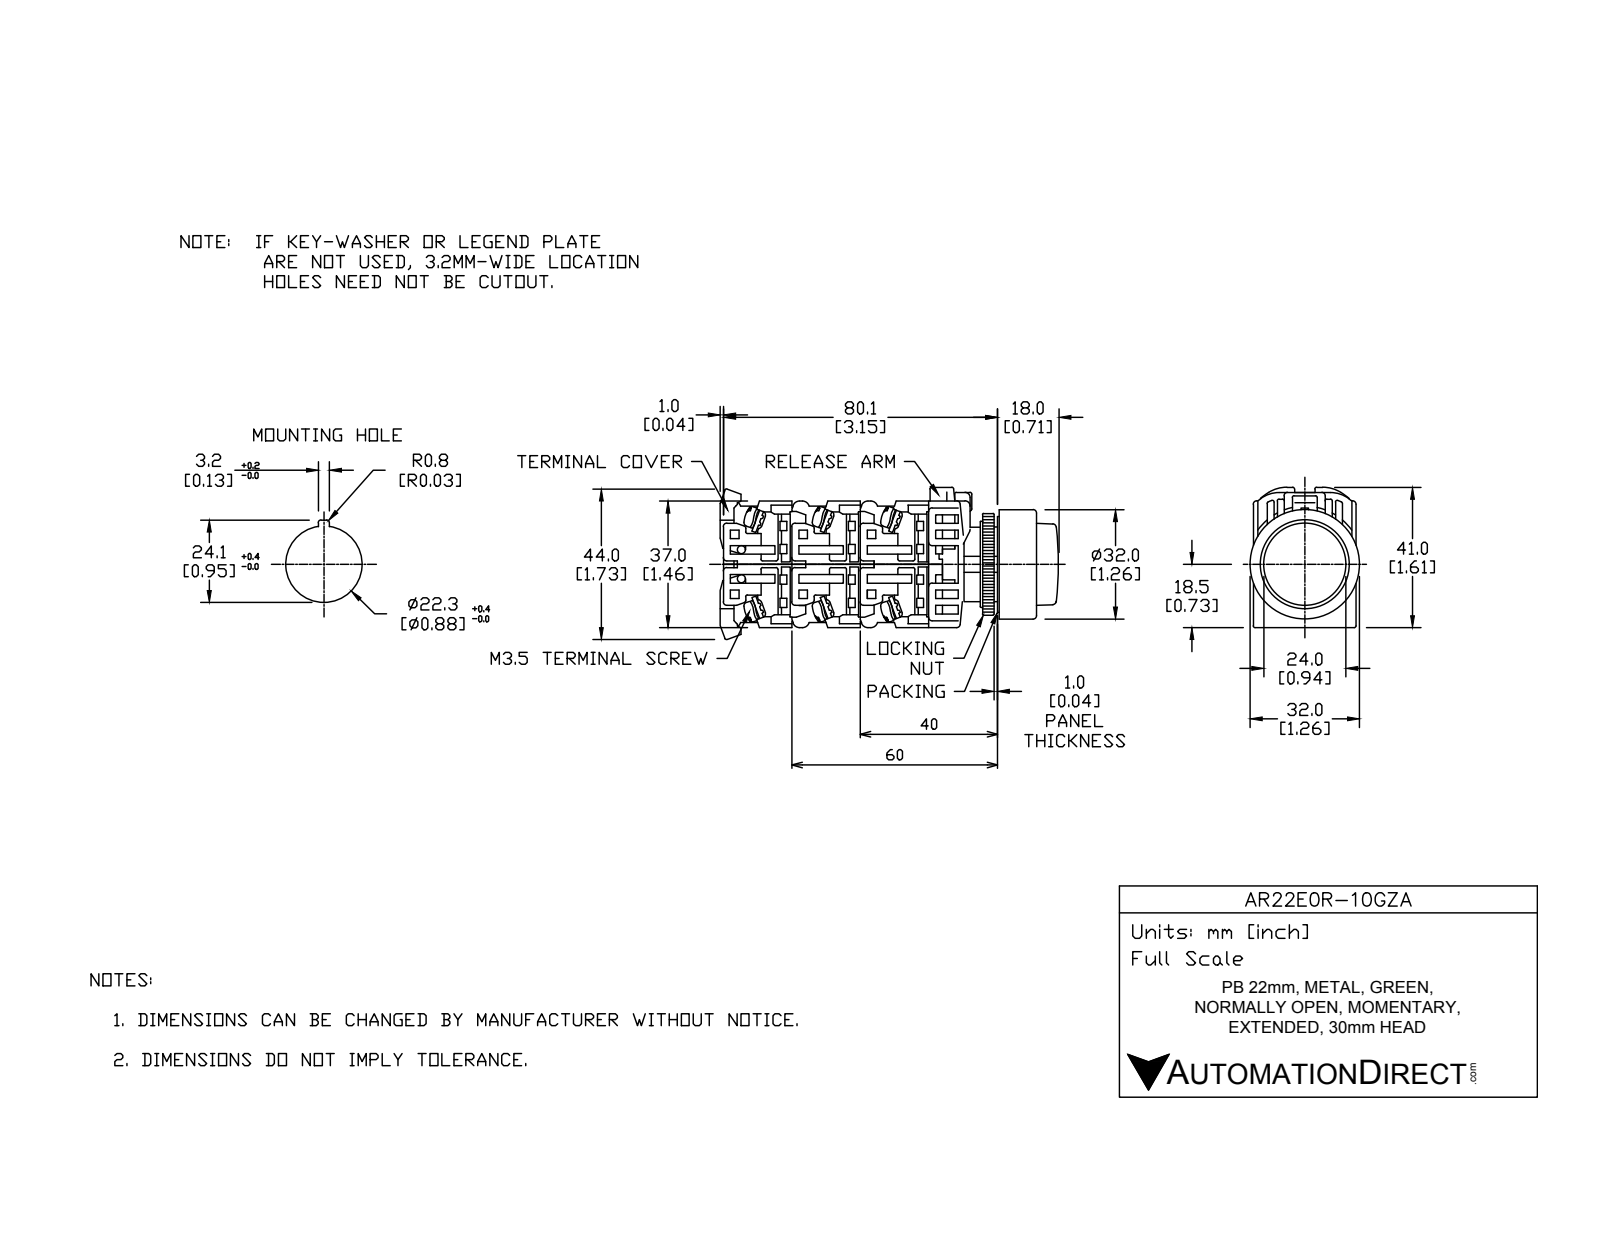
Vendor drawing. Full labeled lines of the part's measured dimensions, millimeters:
Part name (STEP PRODUCT): AR22E0R-10GZA
STEP written by: SolidWorks 2017 (AUTOMOTIVE_DESIGN)
Units: millimetres
Bodies: 12 solids, 297 faces (201 planar, 74 cylindrical, 22 other)
Overall size (bounding box): 59.75 × 41 × 32
Volume: 30 443 mm³ · Surface area: 19 885 mm²
Round holes (diameter × count): ⌀21.8 ×1, ⌀22 ×1, ⌀25 ×1, ⌀31 ×1
Round bosses / shafts (diameter × count): ⌀5 ×2, ⌀32 ×1, ⌀30.5 ×1, ⌀29.8 ×1, ⌀24 ×1, ⌀23.8 ×1, ⌀21.75 ×1, ⌀17 ×1
Partial cylindrical surfaces — rounded edges, fillets, slot ends (radius × count): R0.5 ×23, R1.75 ×4, R5 ×4, R4 ×2, R16.59 ×1, R17.59 ×1
Main face-to-face distances: 1, 28.5, 18, 3, 2, 29, 30, 10.5, 8, 20.5
